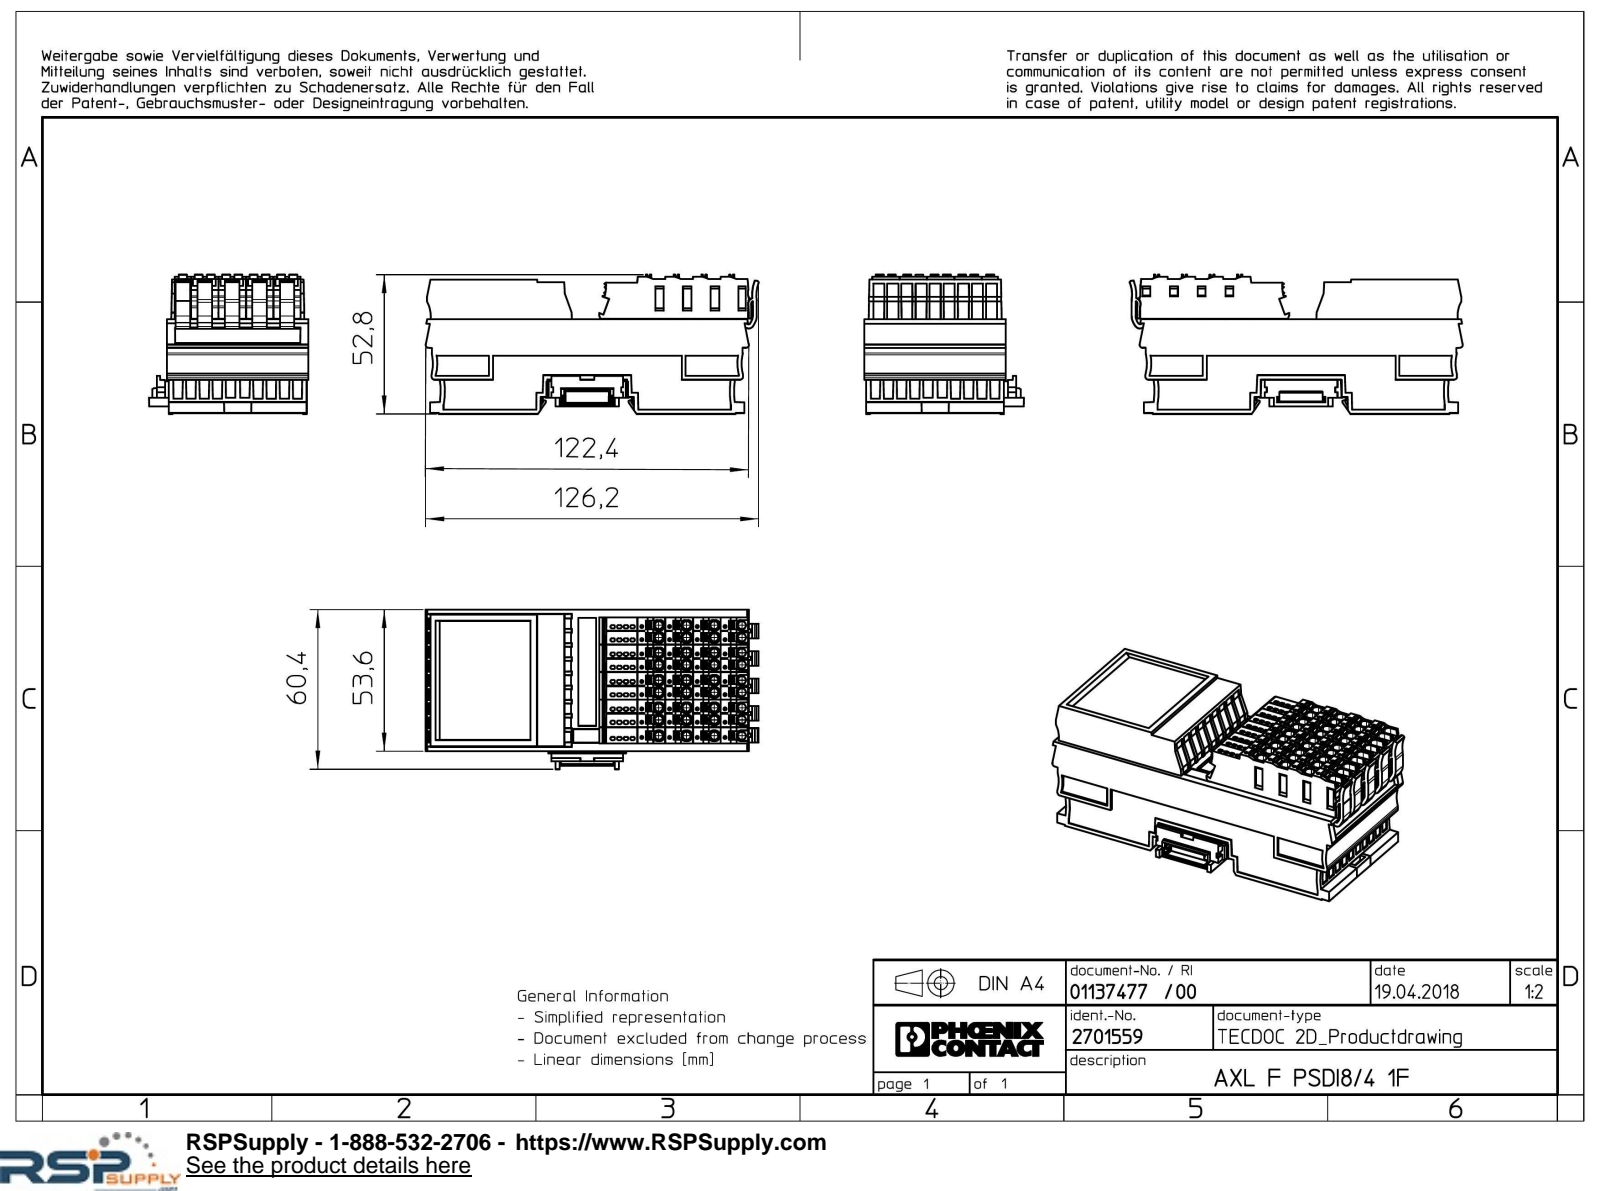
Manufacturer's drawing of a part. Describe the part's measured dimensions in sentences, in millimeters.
The part is named "FIBO_COLOR_CODE_BU5012-select; FIBO_F_YE1018-select; FIBO_P_SP1.5_SINGLE_PWR...-select; FIBO_P_SP_TWIN_YE1018-select (+2 more)". Its 3-D file was written by "Creo Elements/Direct Modeling 20.1A 29-Sep-2018 (C) Parametric Technology GmbH (AUTOMOTIVE_DESIGN)". It is 8 solids with 3724 faces: 3023 planar, 621 cylindrical and 80 other. Overall it measures 126.17 by 60.4 by 52.75 millimeters. Its volume is 282 146 cubic millimeters and its surface area 71 483 square millimeters. Round holes: 36 of diameter 1.2. Partial cylindrical surfaces (rounded edges, fillets, slot ends): 145 of radius 0.5, 126 of radius 1.5, 20 of radius 0.1, 10 of radius 1, 6 of radius 12.6, 5 of radius 3, 3 of radius 2, 2 of radius 0.3. The main face-to-face distances are 10.4, 20.8, 10.5, 0.9, 52.7, 31.2, 10.3, 35.45, 15, 20.7. The hole center spacings are 14.78, 10.4, 10.5, 23.43, 11.63, 23.3, 18.64, 11.81.
